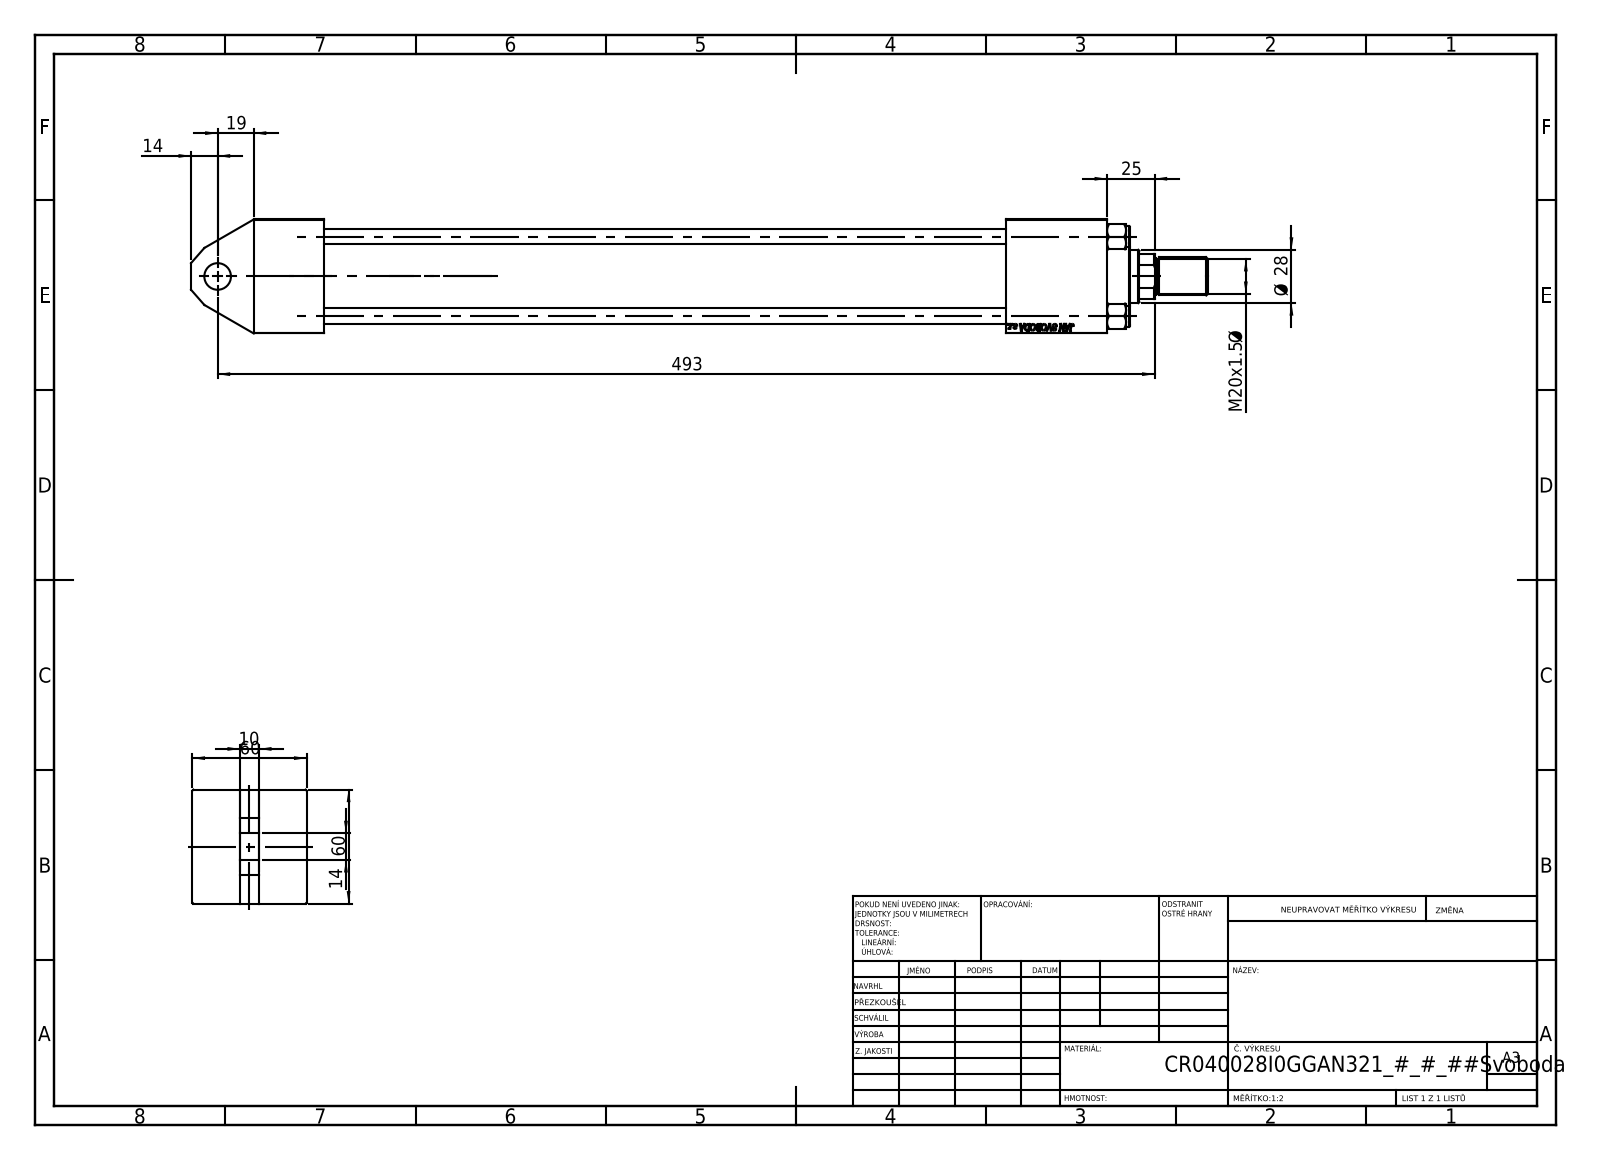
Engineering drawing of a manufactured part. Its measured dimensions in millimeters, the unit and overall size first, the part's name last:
Units: millimetres
Overall size (bounding box): 535 × 60 × 60
Round holes (diameter × count): ⌀8 ×4, ⌀7 ×2, ⌀16.66 ×2, ⌀24 ×2, ⌀14 ×1, ⌀18.5 ×1, ⌀28 ×1, ⌀31 ×1, ⌀40 ×1, ⌀45 ×1
Round bosses / shafts (diameter × count): ⌀11 ×4, ⌀46 ×1, ⌀42 ×1, ⌀20 ×1, ⌀18 ×1
Partial cylindrical surfaces — rounded edges, fillets, slot ends (radius × count): R13.5 ×1
Main face-to-face distances: 60, 37, 25, 53, 35, 396, 359, 449, 412, 420.3
Hole centre spacings: 29.49, 41.7, 58.97, 393.5
Volume: 816 433 mm³ · Surface area: 256 177 mm²
Bodies: 12 solids, 1092 faces (506 planar, 84 cylindrical, 502 other)
Part name (STEP PRODUCT): V215_VC_A; NUT_M5_I; ROD_END_AH; V215CR_VCP_I (+2 more)
STEP written by: SolidWorks 2019 (CONFIG_CONTROL_DESIGN)
